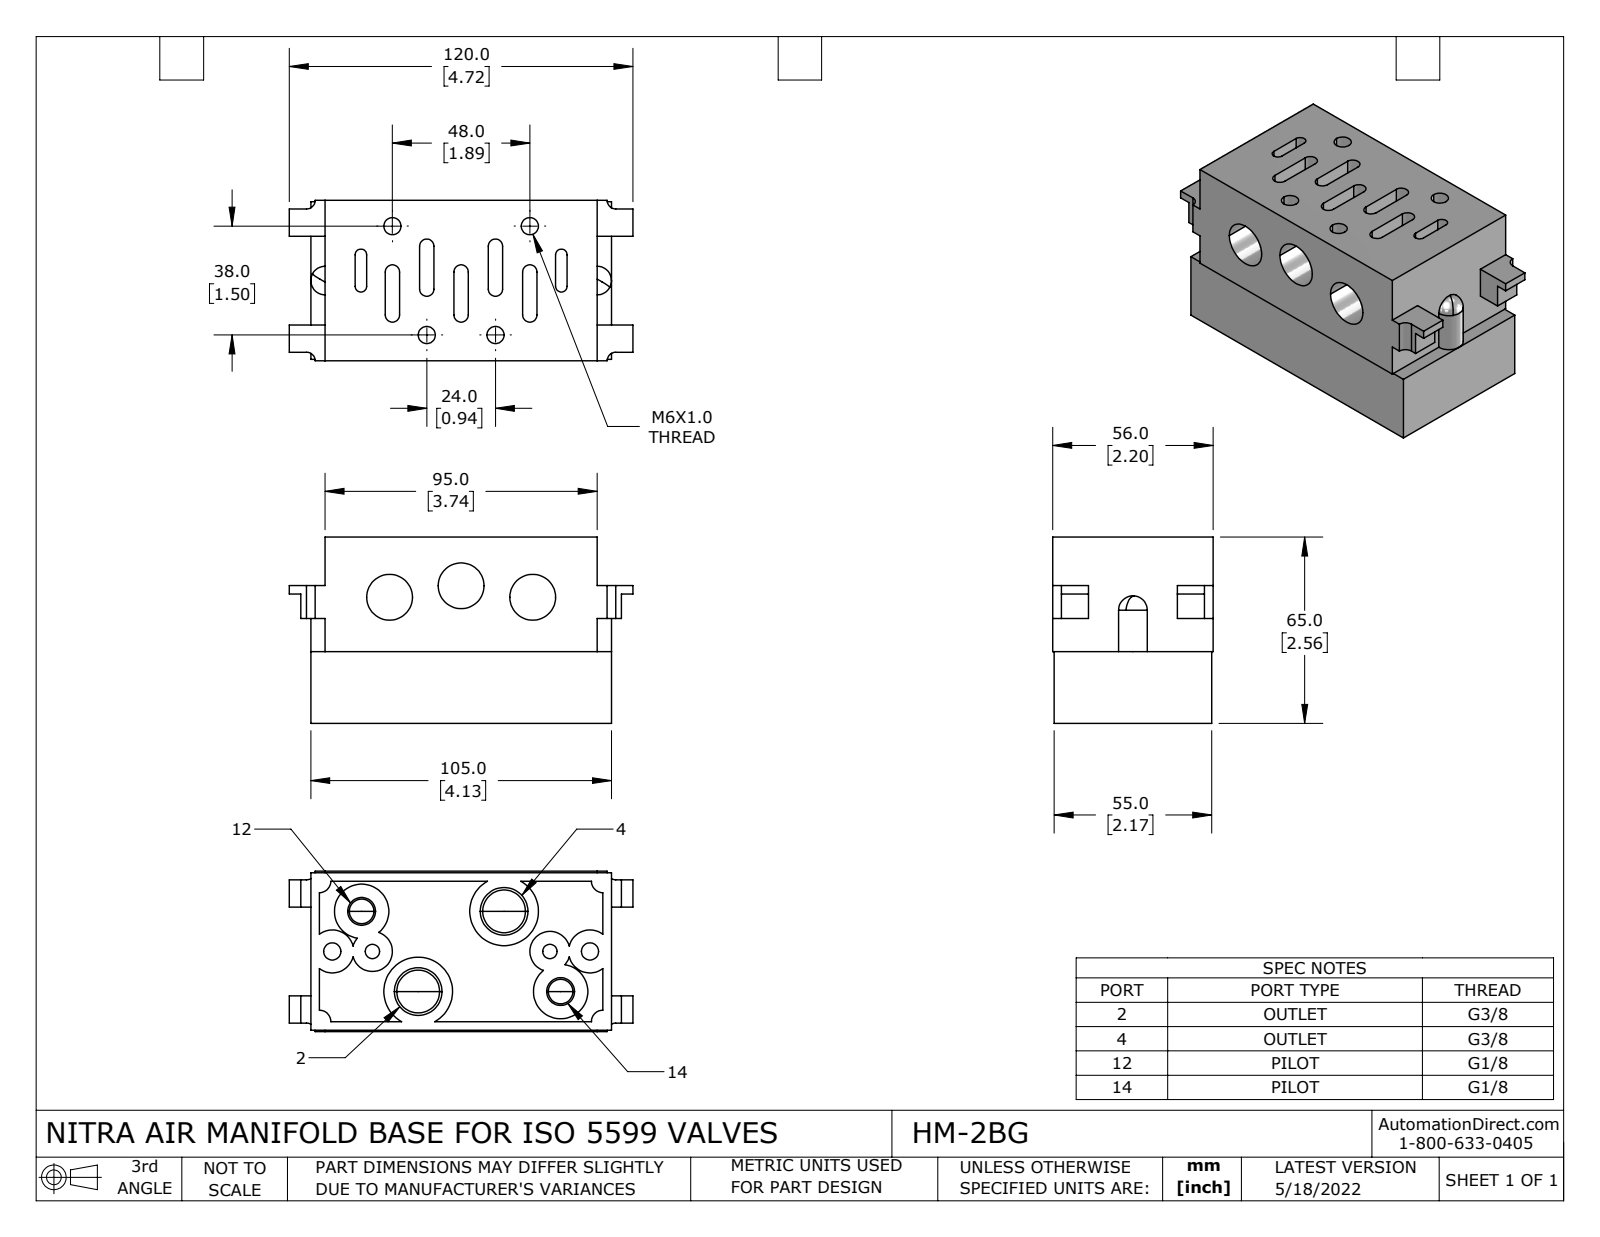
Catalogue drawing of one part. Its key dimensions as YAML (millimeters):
part_name: "HM-2BG"
step_written_by: "SolidWorks 2021 (CONFIG_CONTROL_DESIGN)"
units: millimeters
bodies: {solids: 1, faces: 177, planar: 85, cylindrical: 72, other: 20}
overall_size: [120, 65, 56]
volume: 255341
surface_area: 60152
round_holes:
  - {diameter: 6, count: 6}
  - {diameter: 16, count: 3}
  - {diameter: 21, count: 3}
  - {diameter: 5, count: 2}
  - {diameter: 8.57, count: 2}
  - {diameter: 14.95, count: 2}
round_bosses_or_shafts:
  - {diameter: 24, count: 2}
  - {diameter: 19, count: 2}
partial_cylinders:
  - {radius: 2.5, count: 10}
  - {radius: 2, count: 4}
  - {radius: 3, count: 4}
  - {radius: 4, count: 4}
  - {radius: 5, count: 2}
  - {radius: 7, count: 2}
  - {radius: 7.5, count: 2}
face_to_face_distances: [0.5, 55.5, 3, 5, 52.5, 3.5, 52, 45, 56, 55]
hole_center_spacings: [14, 14.49, 17.35, 20.25, 21.26, 25.32, 26.87, 28.32]
